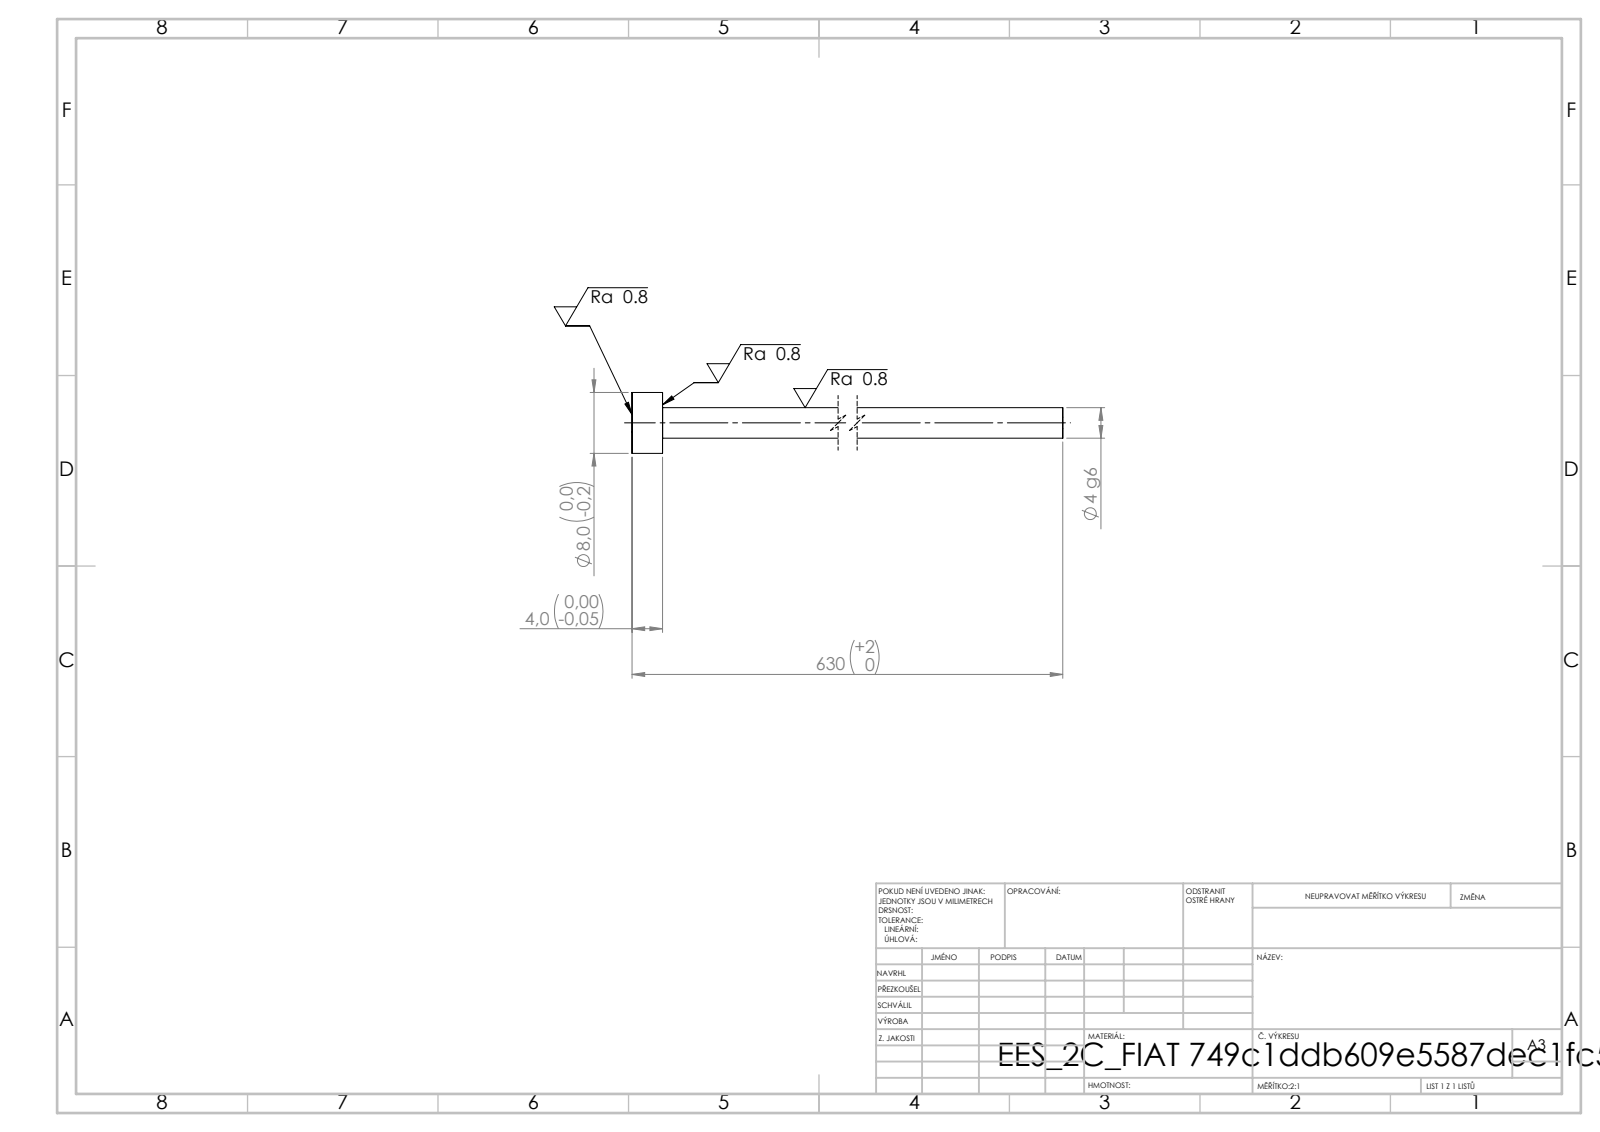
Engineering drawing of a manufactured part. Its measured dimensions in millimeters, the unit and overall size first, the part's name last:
Units: millimetres
Overall size (bounding box): 630 × 8 × 8
Round bosses / shafts (diameter × count): ⌀8 ×1, ⌀4 ×1
Main face-to-face distances: 4, 630, 626
Volume: 8 068 mm³ · Surface area: 8 068 mm²
Bodies: 1 solid, 7 faces (3 planar, 4 cylindrical, 0 other)
STEP written by: SolidWorks 2019 (CONFIG_CONTROL_DESIGN)
